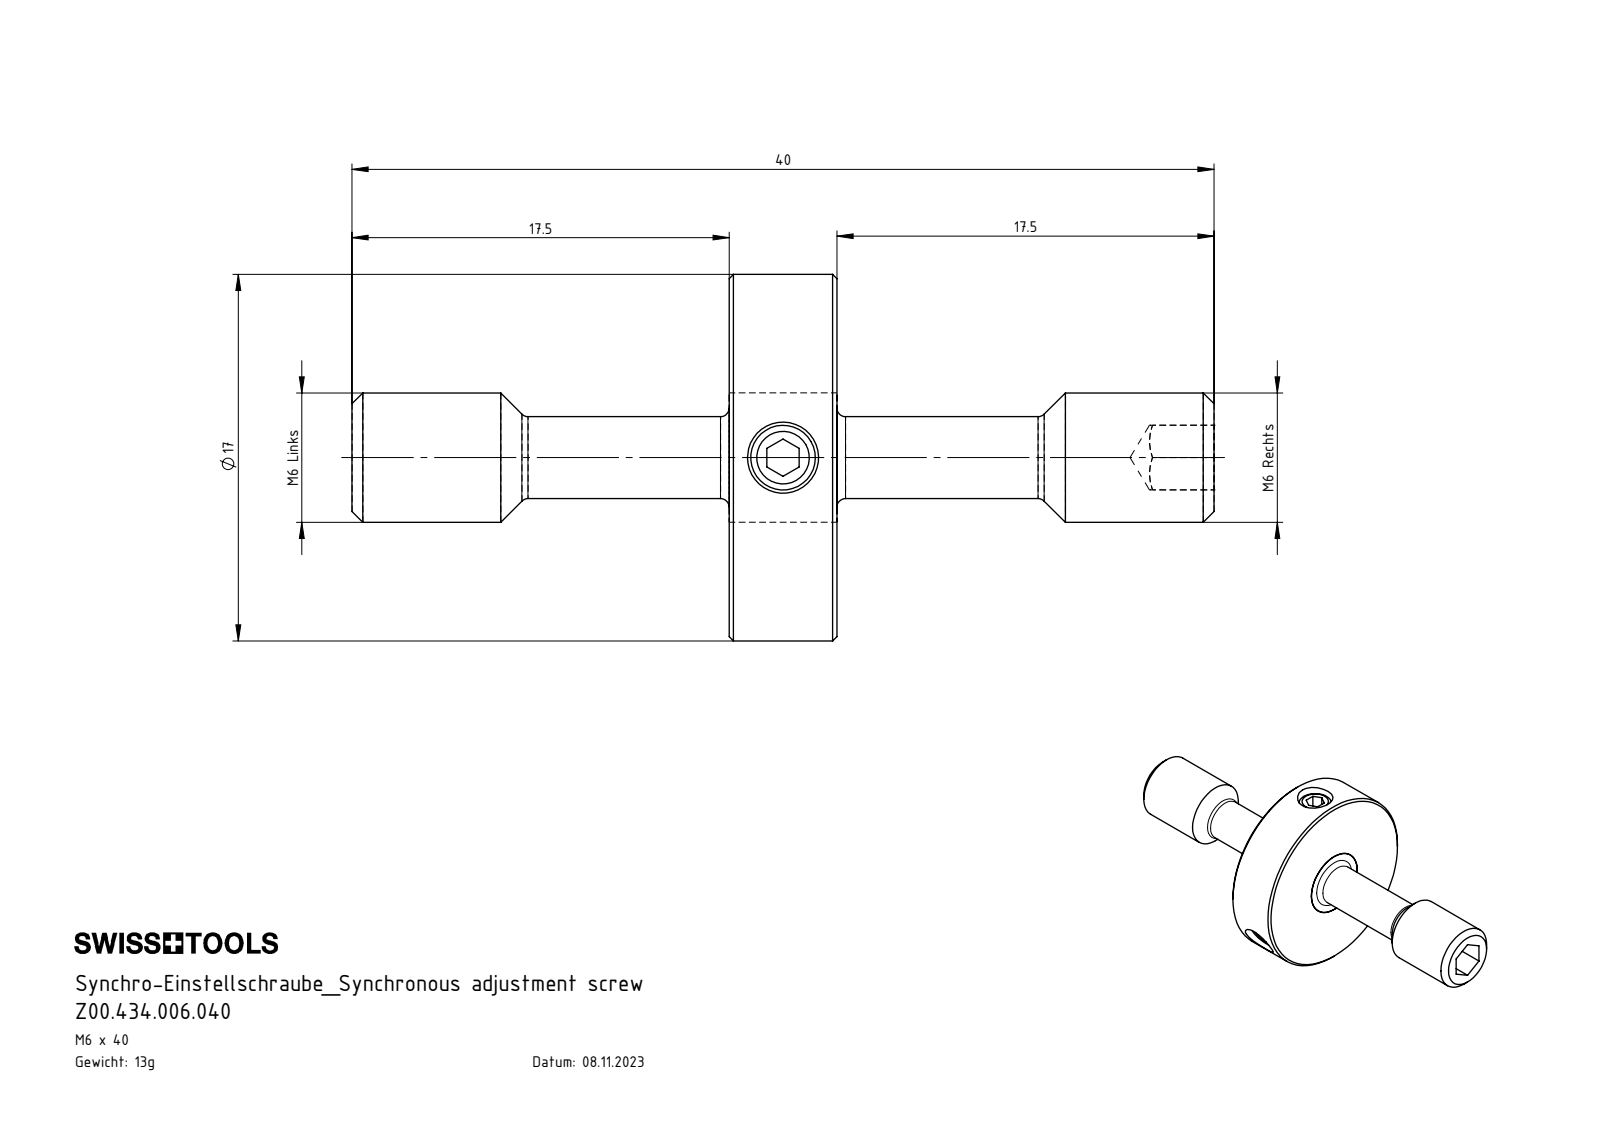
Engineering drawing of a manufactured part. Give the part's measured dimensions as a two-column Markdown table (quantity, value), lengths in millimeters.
| quantity | value |
| --- | --- |
| part name | ISO 4026 - M3 x 5; Z42-ER3.002.005_A; Z00.434.006.040; Z42-ER3.001.040_A |
| STEP written by | SolidWorks 2022 (AUTOMOTIVE_DESIGN) |
| units | millimeters |
| bodies | 5 solids, 99 faces (39 planar, 26 cylindrical, 34 other) |
| overall size | 40 × 17 × 17 |
| volume | 1 699 mm³ |
| surface area | 1 807 mm² |
| round holes (diameter × count) | 3.3 × 3 |
| round bosses / shafts (diameter × count) | 3 × 3, 17 × 1, 6 × 1, 3.8 × 1 |
| main face-to-face distances | 5, 17.5, 22.5, 3, 1.5, 40, 19.25, 20.75, 1.75, 3.25 |
